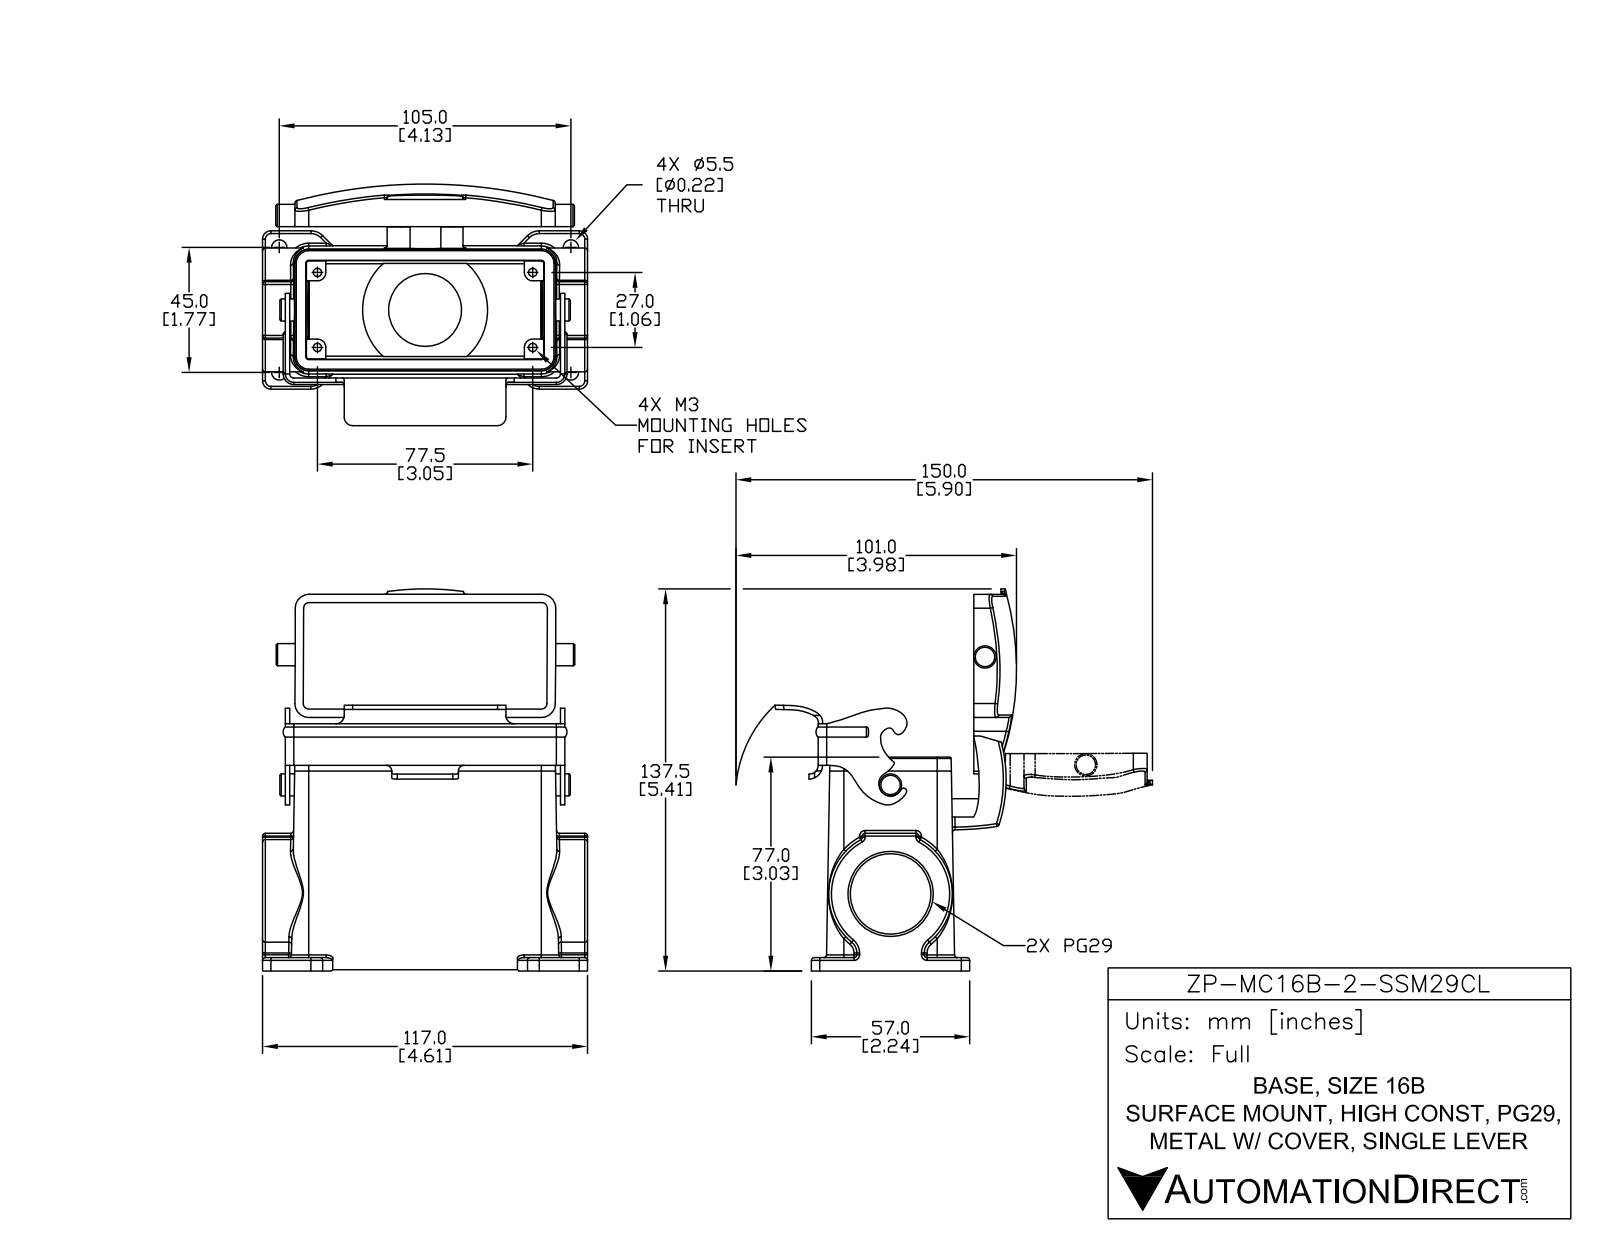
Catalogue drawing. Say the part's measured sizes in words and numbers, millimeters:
The part is named "ZP-MC16B-2-SSM29CL". Its 3-D file was written by "SolidWorks 2014 (AUTOMOTIVE_DESIGN)". It is 3 solids with 455 faces: 158 planar, 176 cylindrical and 121 other. Overall it measures 135.49 by 117 by 80.58 millimeters. Its volume is 176 580 cubic millimeters and its surface area 82 357 square millimeters. Round holes: 4 of diameter 3, 4 of diameter 5.5, 1 of diameter 2, 1 of diameter 25.23, 1 of diameter 30, 1 of diameter 35.5. Round bosses or shafts: 1 of diameter 8, 1 of diameter 7.95. Partial cylindrical surfaces (rounded edges, fillets, slot ends): 26 of radius 1, 12 of radius 3, 8 of radius 2, 6 of radius 5, 4 of radius 0.5, 4 of radius 6, 2 of radius 1.5, 2 of radius 3.06. The main face-to-face distances are 39.67, 0.5, 1.56, 6.7, 6.2, 3, 9.75, 107.25, 40.48, 8.19. The hole center spacings are 16.43, 38.54, 41.03, 57.12, 91.69, 98.09, 27, 45.
